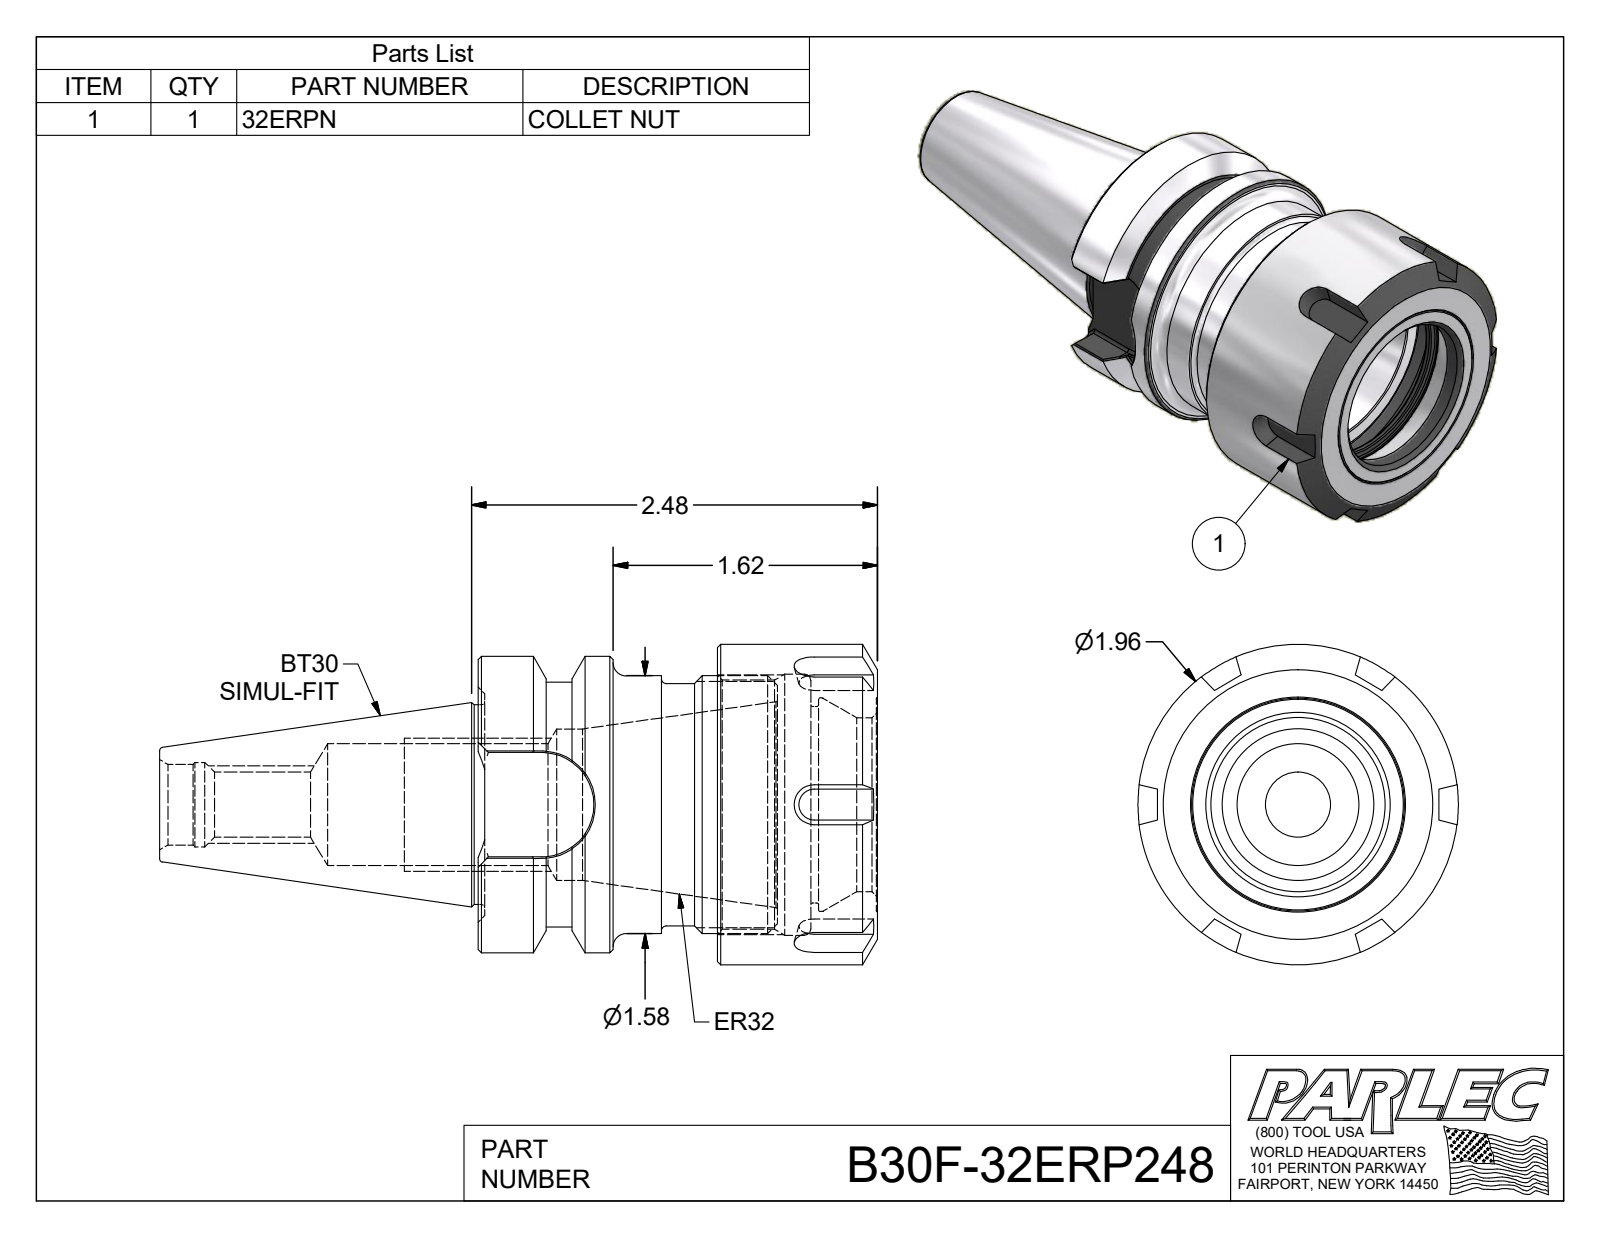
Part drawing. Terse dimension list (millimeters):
name: B30F-32ER236-1; 32ERPN; B30F-32ERP248
written by: Autodesk Inventor 2016 (AUTOMOTIVE_DESIGN)
unit: mm
bodies: 2 solids, 141 faces (48 planar, 30 cylindrical, 63 other)
size: 111.4 × 49.73 × 49.73
volume: 73 572 mm³; area: 28 021 mm²
holes: 1× ⌀10.11, 1× ⌀12.51, 1× ⌀13.12, 1× ⌀18.92, 1× ⌀23.49, 1× ⌀27, 1× ⌀30.48, 1× ⌀33.15, 1× ⌀38.68, 1× ⌀40.51
bosses: 1× ⌀49.73, 1× ⌀46, 1× ⌀40, 1× ⌀40, 1× ⌀37.59, 1× ⌀30.99
rounds: 8× R0.51, 1× R8.09, 1× R19
face distances: 24.84, 14.5, 10.34, 37.14, 51.64, 61.98, 46.49, 9.35, 5.15, 15.49
